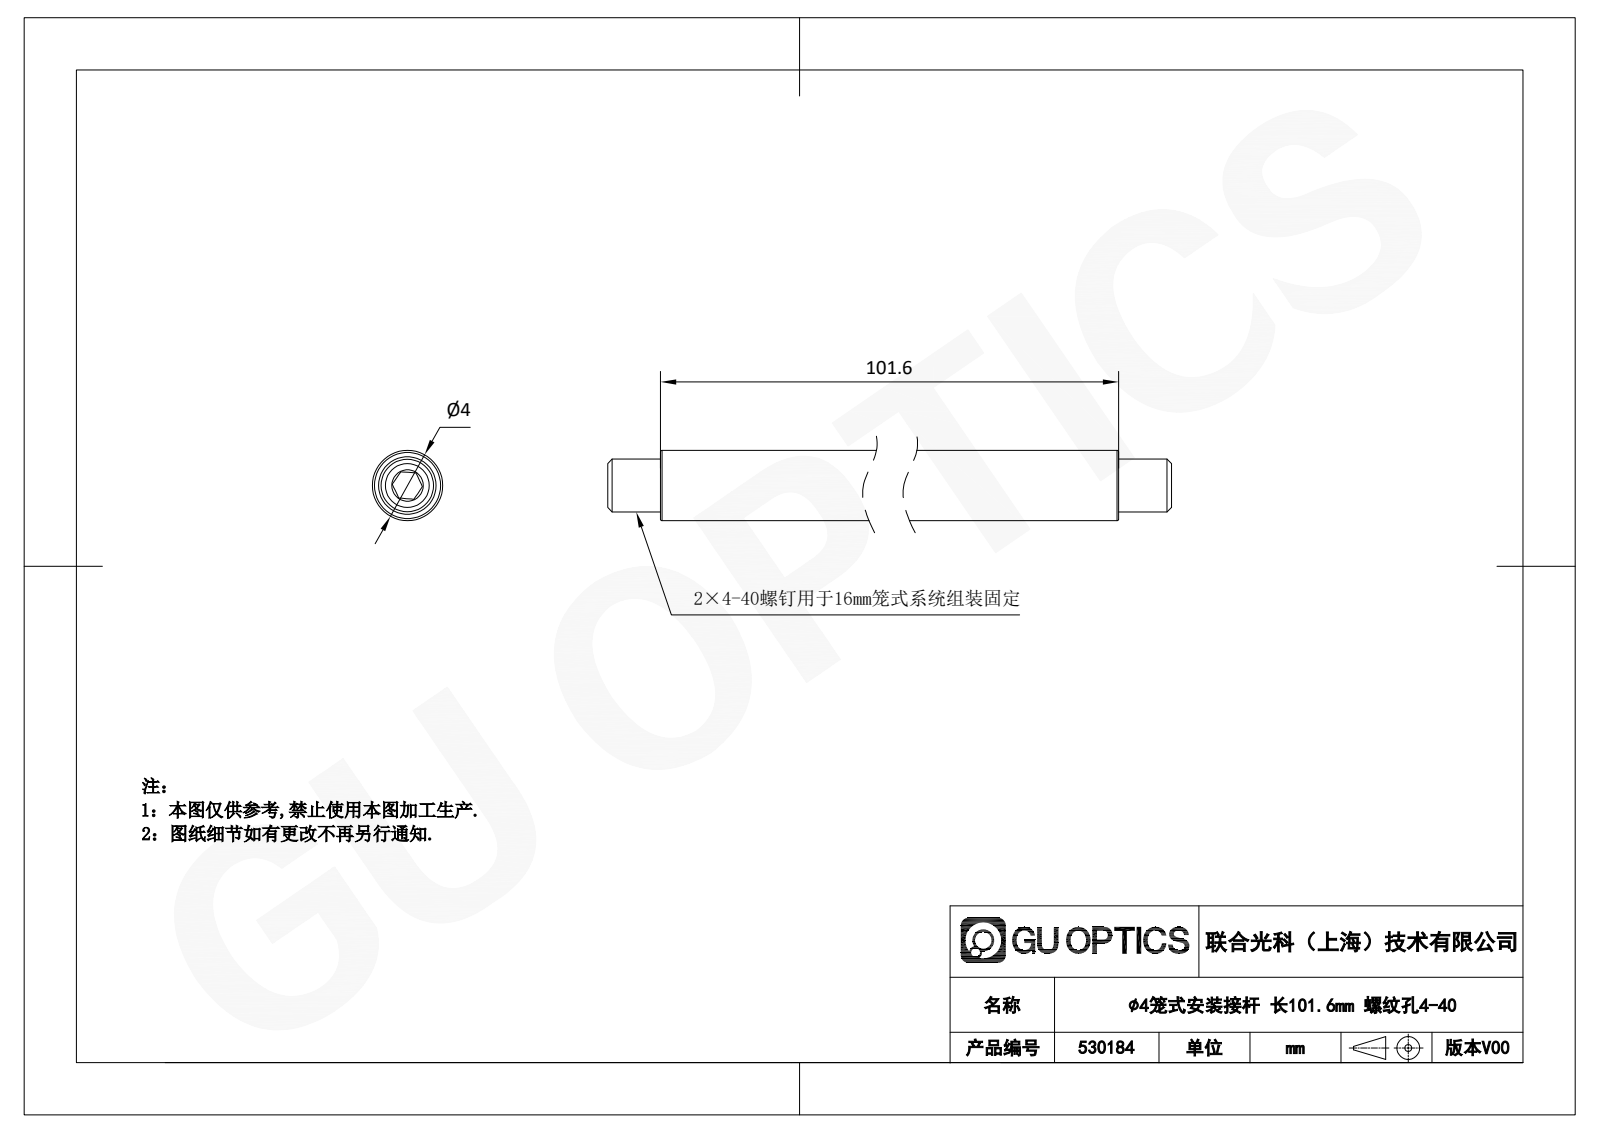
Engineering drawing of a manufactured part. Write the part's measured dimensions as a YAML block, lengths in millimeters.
part_name: "530184"
step_written_by: "SolidWorks 2020 (CONFIG_CONTROL_DESIGN)"
units: millimeters
bodies: {solids: 3, faces: 37, planar: 20, cylindrical: 5, other: 12}
overall_size: [111.6, 4, 4]
volume: 1326
surface_area: 1566
round_holes:
  - {diameter: 2.5, count: 1}
round_bosses_or_shafts:
  - {diameter: 4, count: 1}
  - {diameter: 3, count: 1}
face_to_face_distances: [3, 98.6, 5, 8, 103.6, 106.6, 1.5, 101.6, 1, 110.6]
